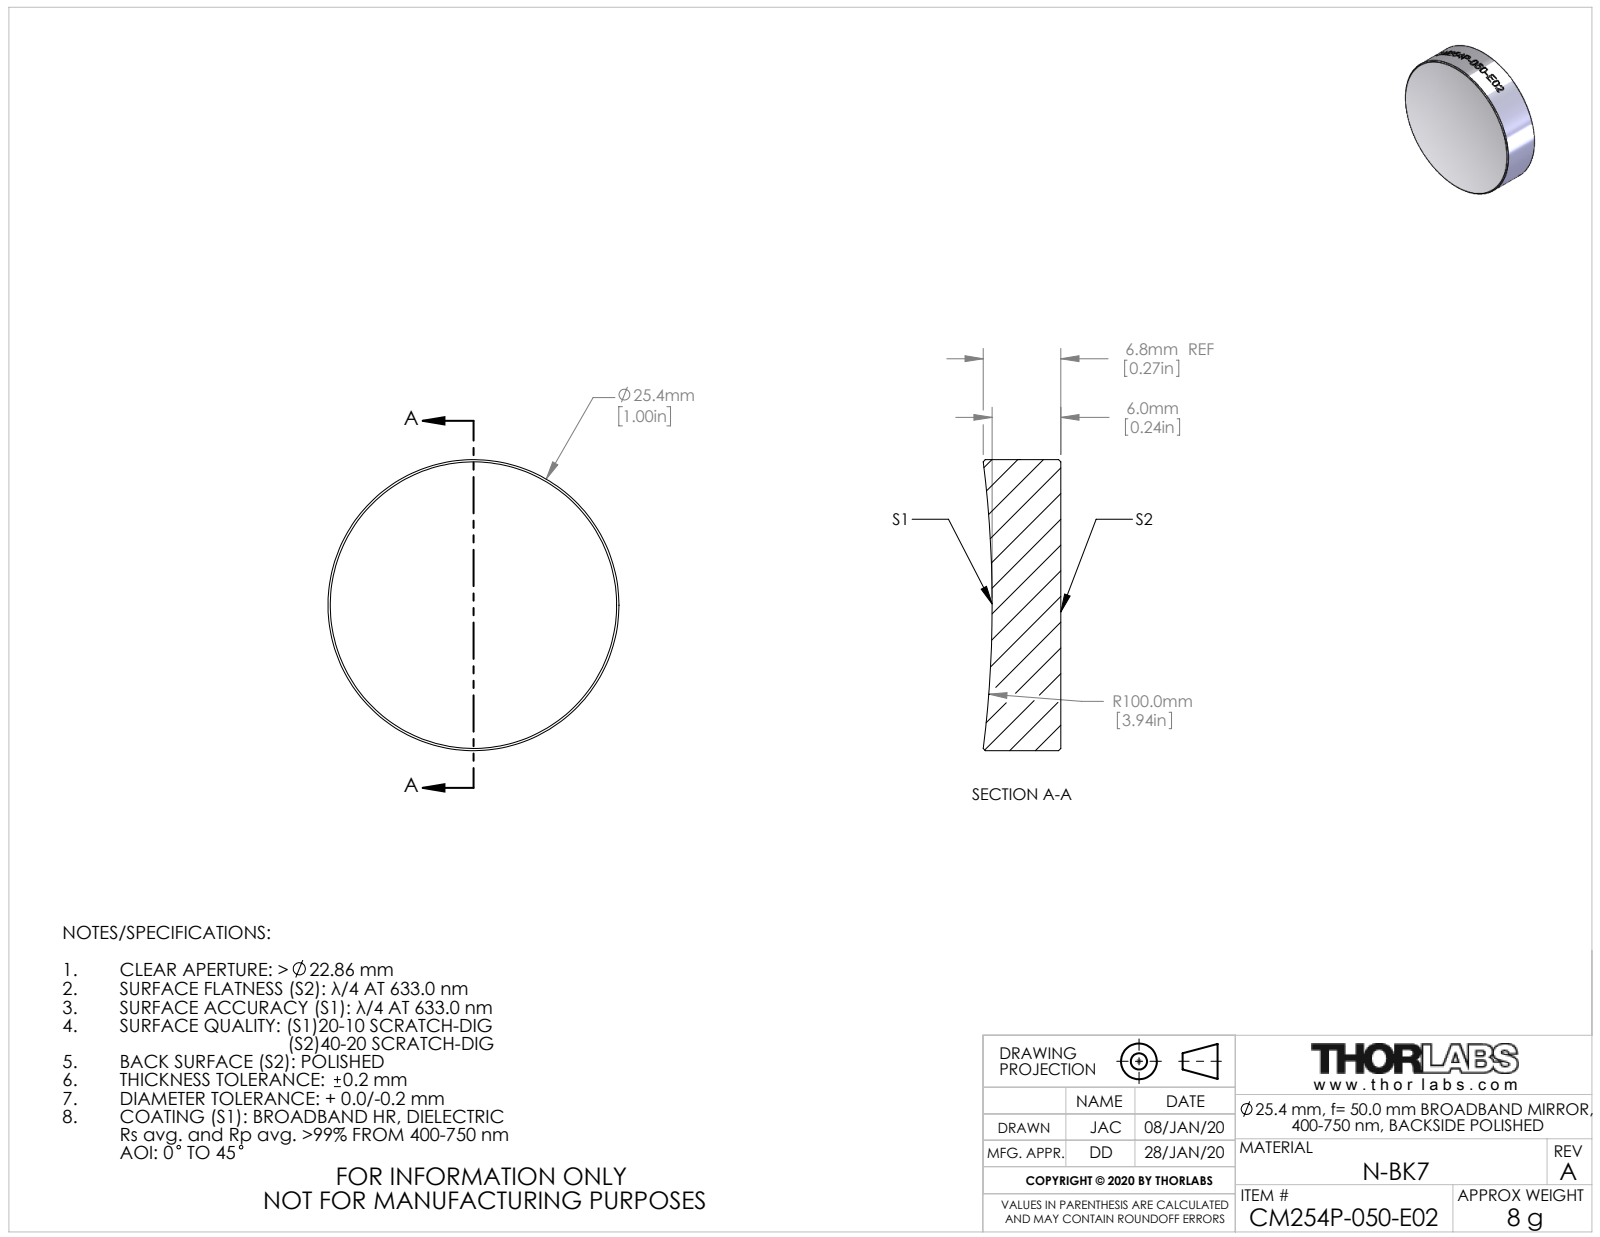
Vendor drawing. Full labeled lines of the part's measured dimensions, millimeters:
Part name (STEP PRODUCT): TTN201331-E0W
STEP written by: SolidWorks 2018 (CONFIG_CONTROL_DESIGN)
Units: millimetres
Bodies: 1 solid, 28 faces (1 planar, 21 cylindrical, 6 other)
Overall size (bounding box): 25.4 × 25.4 × 6.79
Volume: 3 242 mm³ · Surface area: 1 539 mm²
Round bosses / shafts (diameter × count): ⌀25.4 ×1
